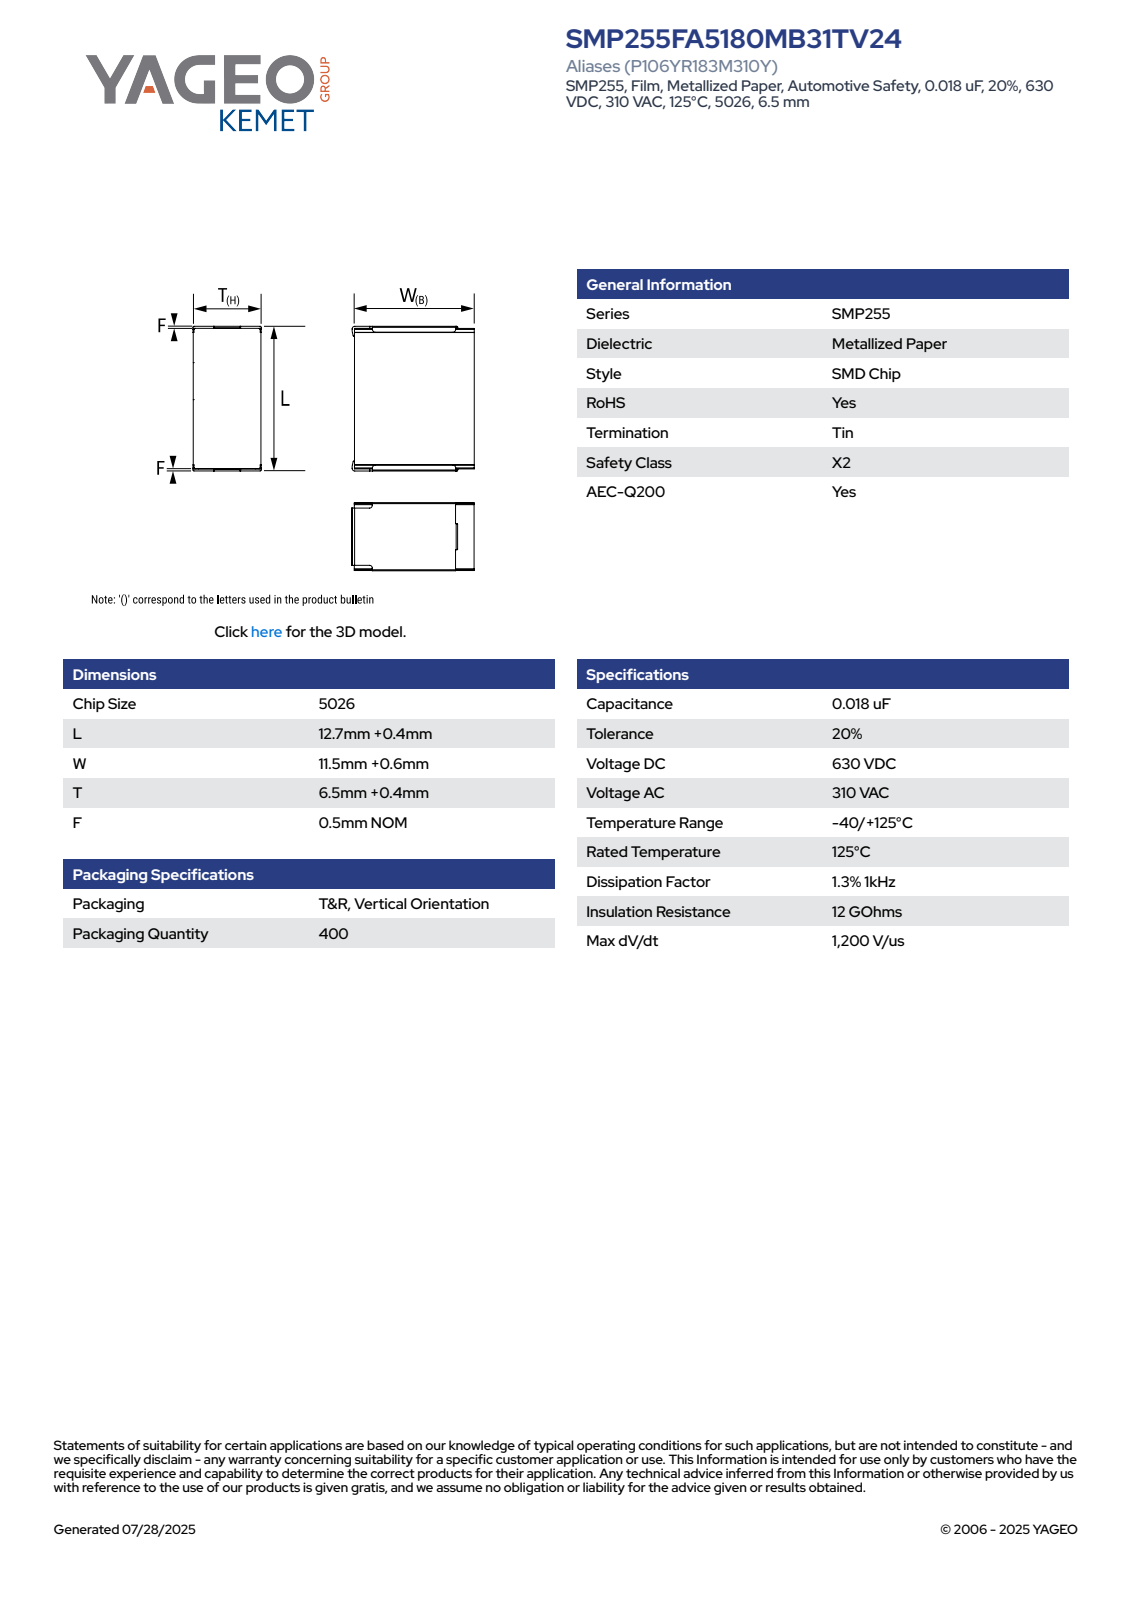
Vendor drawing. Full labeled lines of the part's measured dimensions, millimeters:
Part name (STEP PRODUCT): CFS_KSTD_5026_L13.1W12.1T6.9F0.5
STEP written by: SolidWorks 2021 (AUTOMOTIVE_DESIGN)
Units: millimetres
Bodies: 4 solids, 117 faces (103 planar, 14 cylindrical, 0 other)
Overall size (bounding box): 13.1 × 12.51 × 7.25
Volume: 1 058 mm³ · Surface area: 703 mm²
Partial cylindrical surfaces — rounded edges, fillets, slot ends (radius × count): R0.41 ×10, R0.46 ×4
Main face-to-face distances: 6.9, 11.62, 13.1, 0.5, 12.6, 7.08, 12.1, 0.48, 7.26, 12.5
